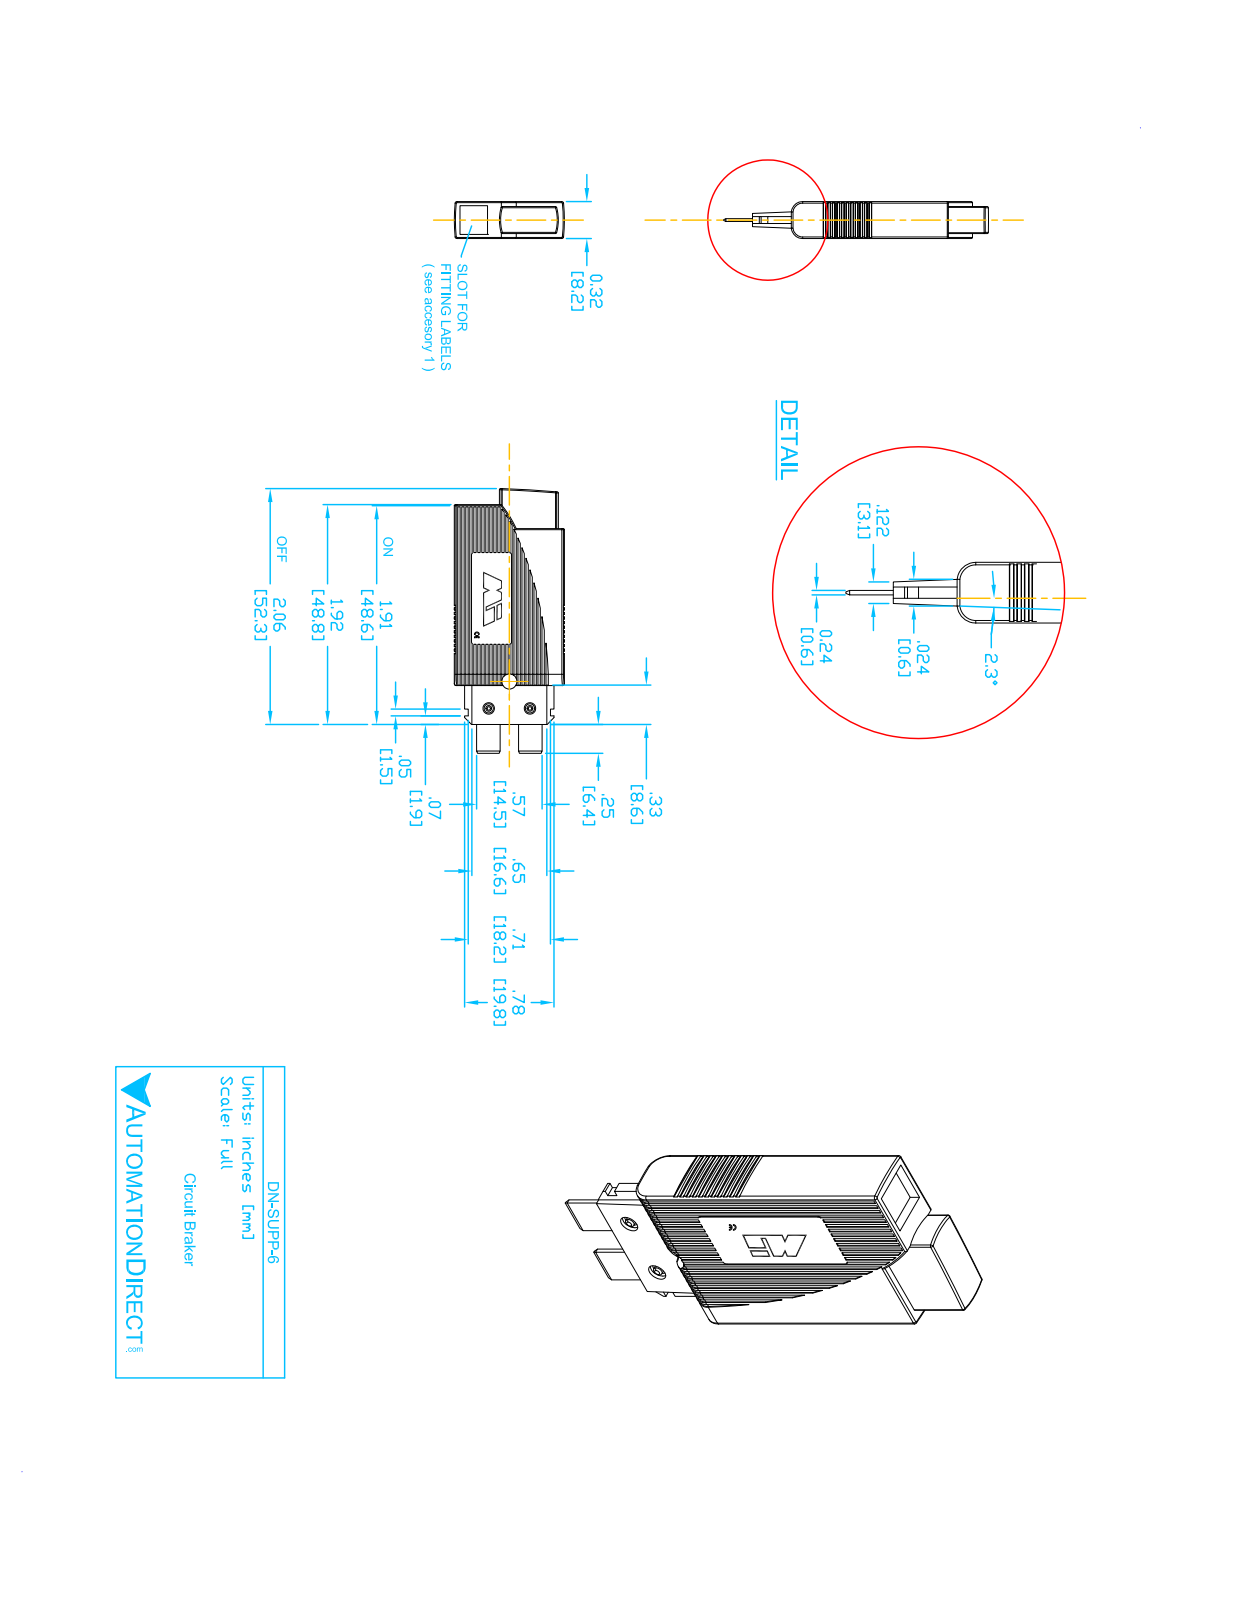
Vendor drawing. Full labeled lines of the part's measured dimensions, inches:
Part name (STEP PRODUCT): DN-SUPP-6
STEP written by: SolidWorks 2017 (AUTOMOTIVE_DESIGN)
Units: inches
Bodies: 1 solid, 95 faces (47 planar, 28 cylindrical, 20 other)
Overall size (bounding box): 2.18 × 0.961 × 0.323
Volume: 0.505 in³ · Surface area: 5.231 in²
Partial cylindrical surfaces — rounded edges, fillets, slot ends (radius × count): R0.012 ×21, R0.157 ×2, R2.165 ×1, R2.331 ×1, R2.362 ×1
Main face-to-face distances: 0.323, 0.961, 0.15, 0.173, 0.031, 0.291, 0.118, 0.142, 0.024, 0.14
